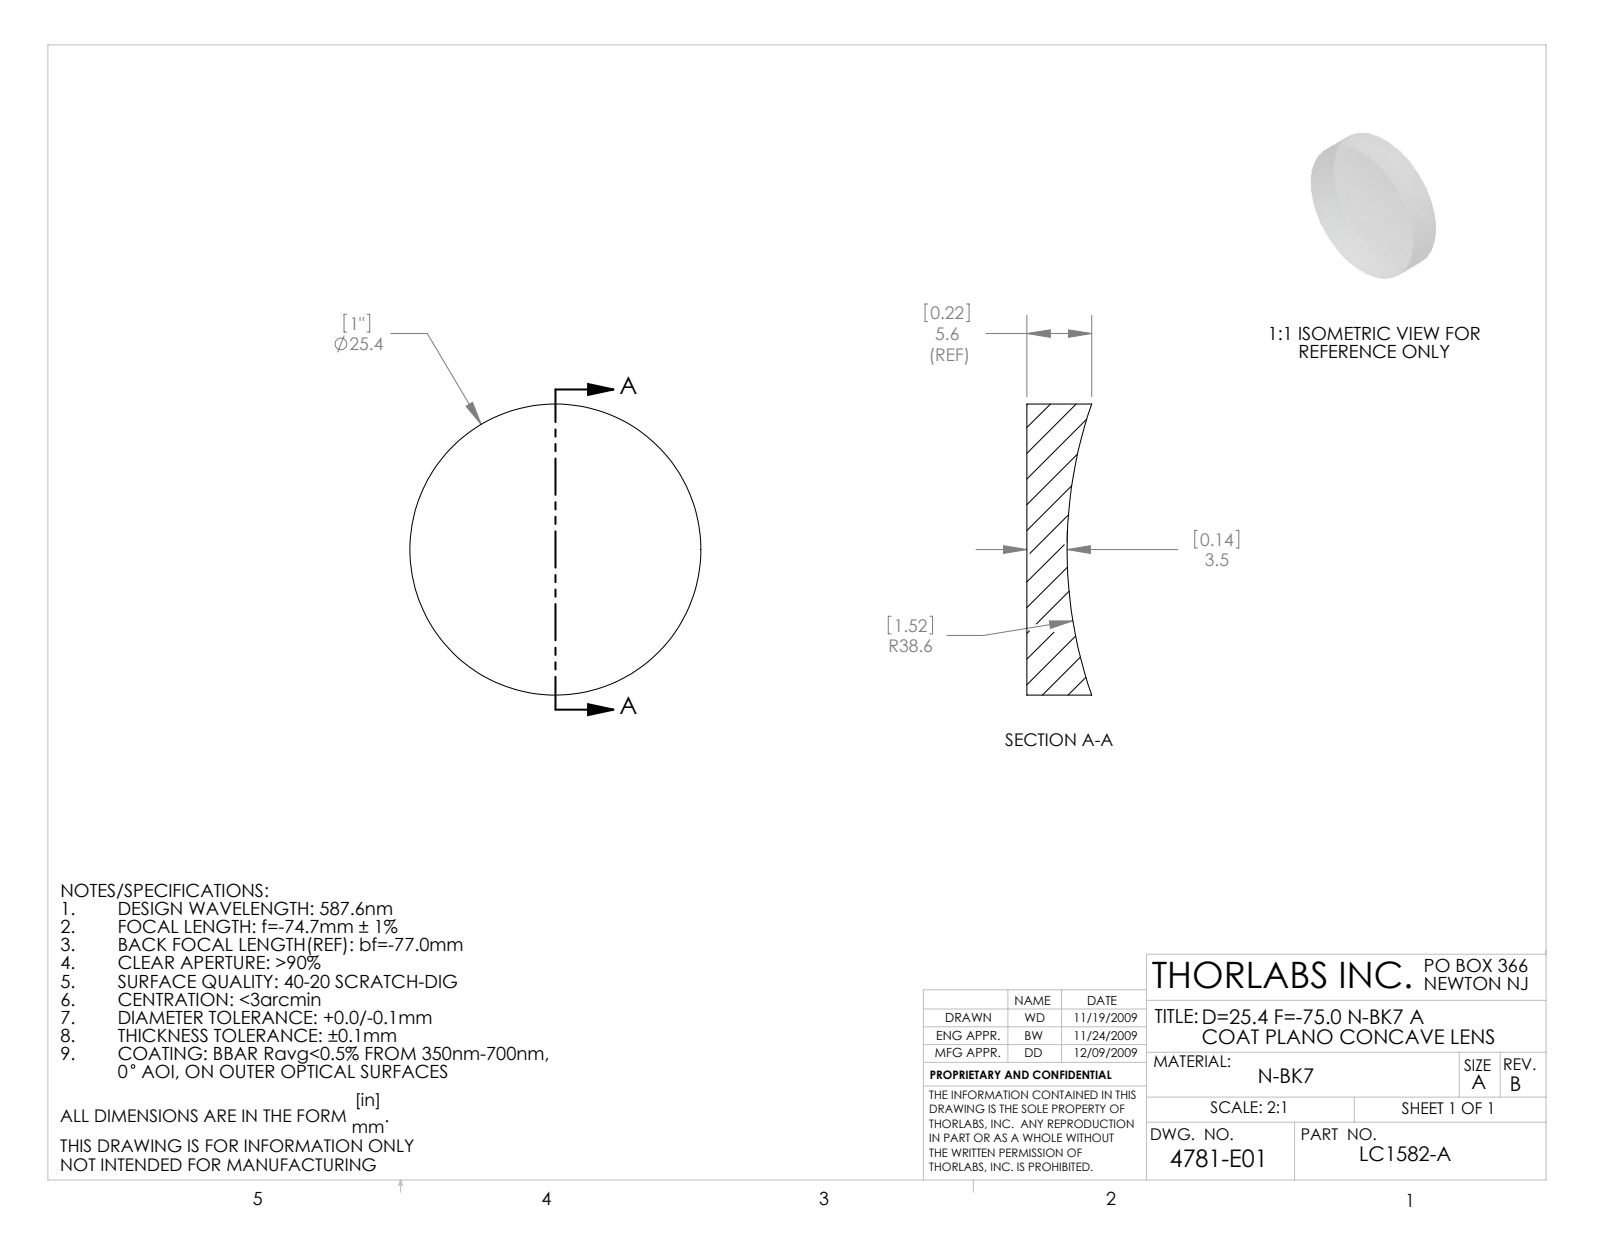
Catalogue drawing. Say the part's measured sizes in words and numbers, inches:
The part is named "4781-E0W". Its 3-D file was written by "SolidWorks 2009 (AUTOMOTIVE_DESIGN)". It is 1 solid with 5 faces: 1 planar, 2 cylindrical and 2 other. Overall it measures 1 by 1 by 0.222 inches. Its volume is 0.141 cubic inches and its surface area 2.292 square inches. Round bosses or shafts: 1 of diameter 1.
